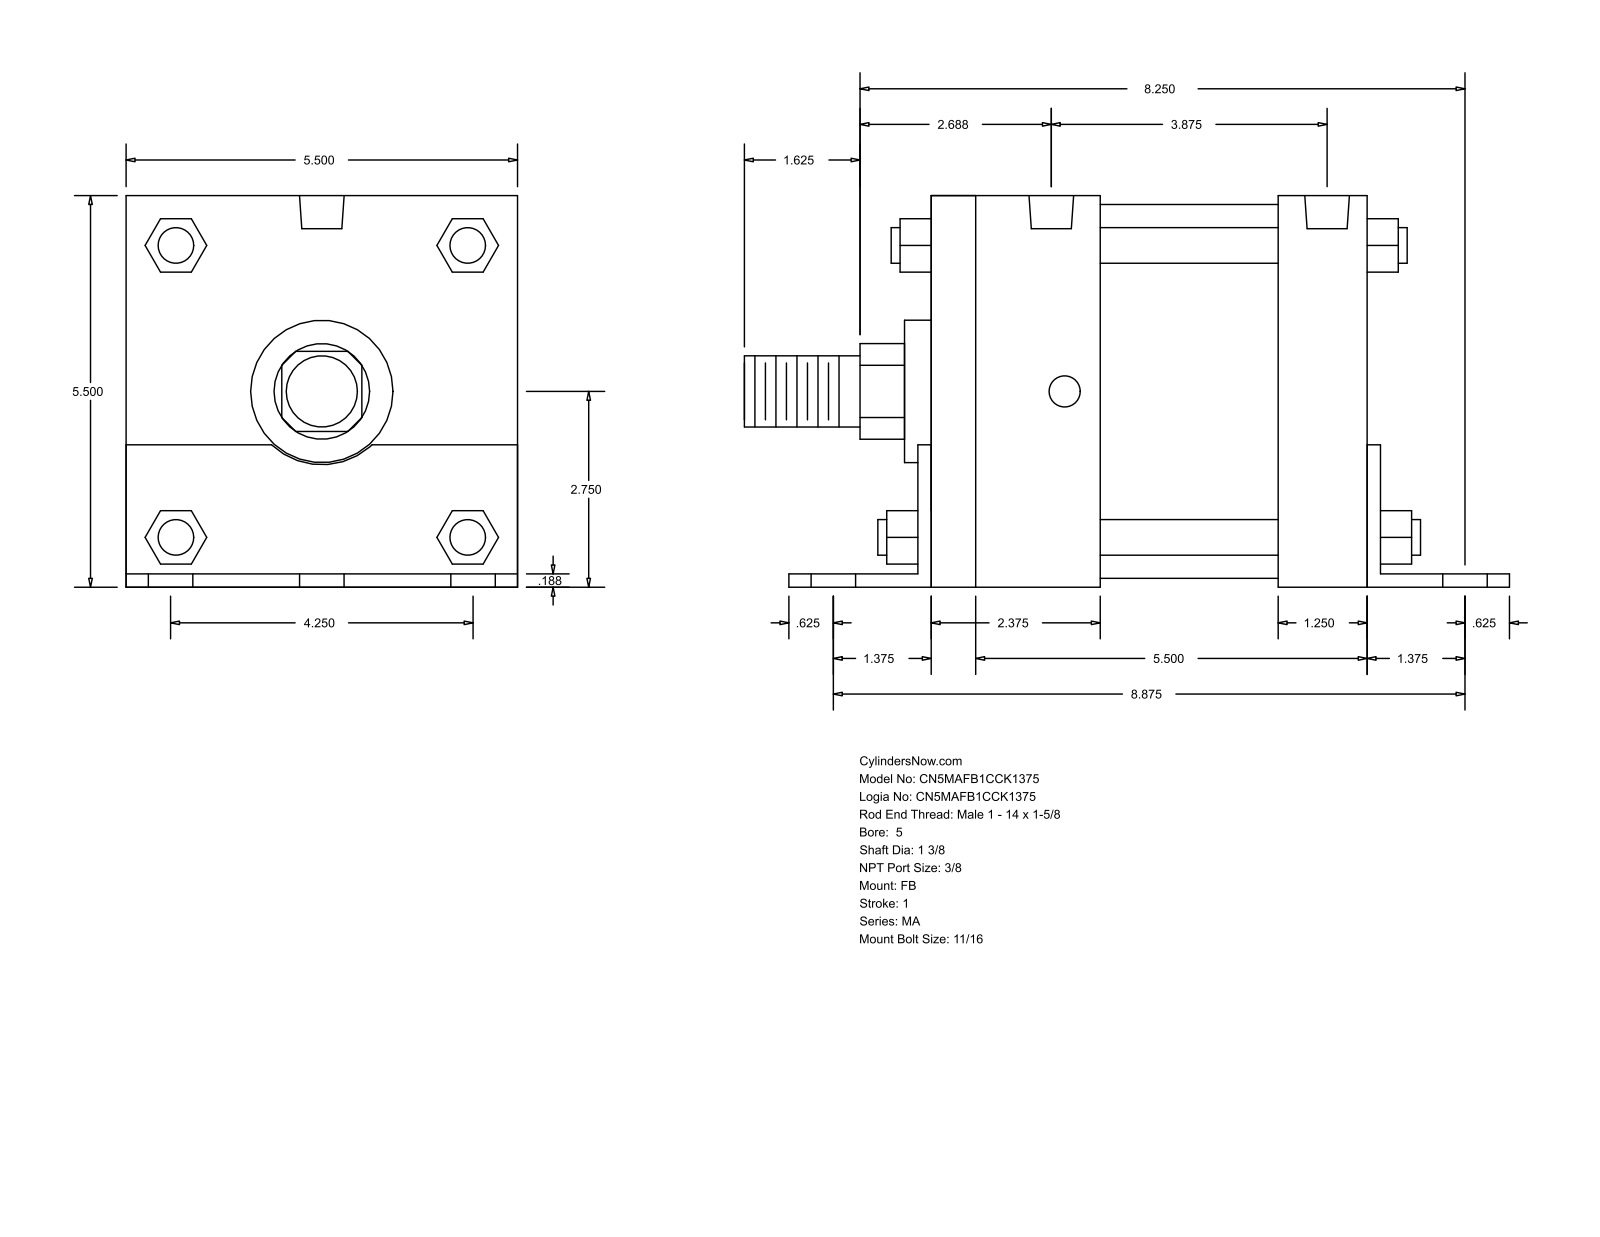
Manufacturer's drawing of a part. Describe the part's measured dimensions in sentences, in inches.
The part is named "MA_FB__0500_1.375". Its 3-D file was written by "GSSL Pune (CONFIG_CONTROL_DESIGN)". It is 0 solids with 140 faces: 105 planar, 35 cylindrical and 0 other. Overall it measures 10.75 by 5.502 by 5.5 inches. Round holes: 6 of diameter 0.687, 4 of diameter 0.437, 2 of diameter 0.627. Round bosses or shafts: 4 of diameter 0.5, 1 of diameter 5.25, 1 of diameter 2, 1 of diameter 1.375, 1 of diameter 1. Partial cylindrical surfaces (rounded edges, fillets, slot ends): 1 of radius 0.672, 1 of radius 1.03. The main face-to-face distances are 5.5, 0.187, 5.502, 0.185, 5.315, 6.125, 0.188, 6.313, 6.312, 6.5. The hole center spacings are 2.125, 9.126, 8.875, 2.876, 3.005, 3.5, 3.728, 3.883.
